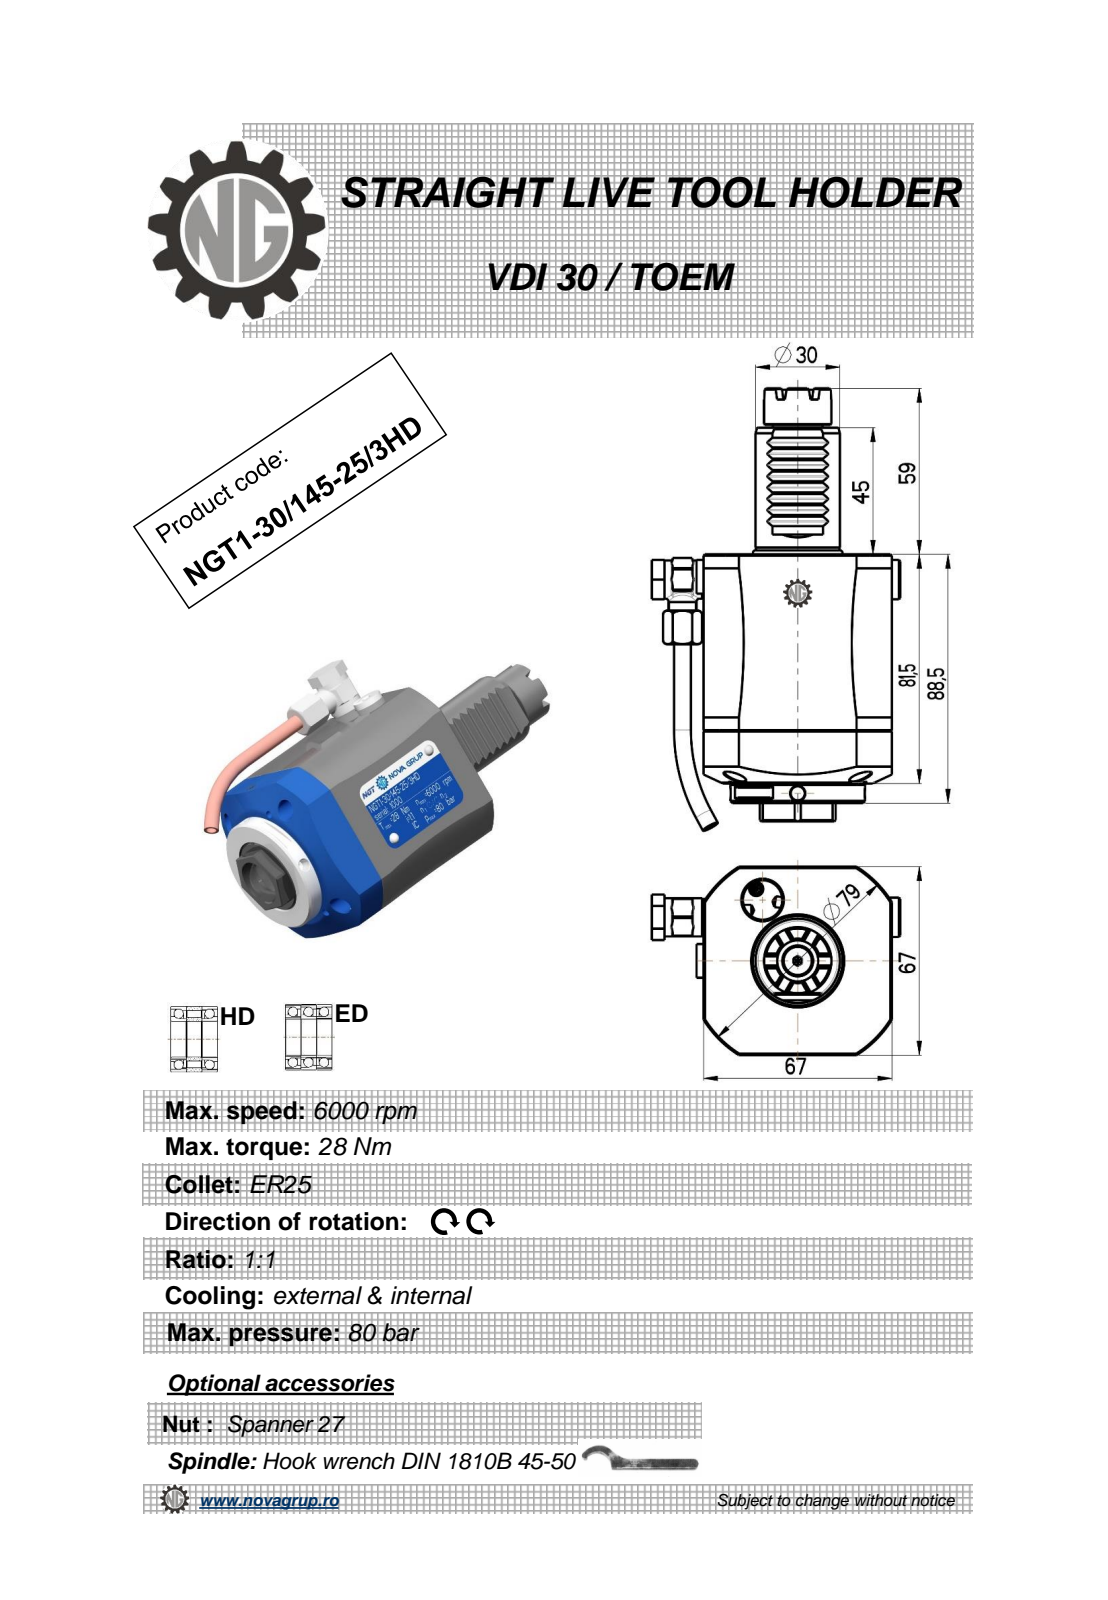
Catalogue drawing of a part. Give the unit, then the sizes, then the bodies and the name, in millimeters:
Units: millimetres
Overall size (bounding box): 157.33 × 88.4 × 67
Round holes (diameter × count): ⌀4 ×3, ⌀5 ×2, ⌀3 ×1, ⌀6 ×1, ⌀6.2 ×1, ⌀9 ×1, ⌀10 ×1, ⌀11 ×1, ⌀18 ×1, ⌀26.5 ×1
Round bosses / shafts (diameter × count): ⌀48 ×1, ⌀30 ×1, ⌀24 ×1, ⌀17.7 ×1, ⌀14 ×1, ⌀13.6 ×1, ⌀13 ×1, ⌀12 ×1
Partial cylindrical surfaces — rounded edges, fillets, slot ends (radius × count): R0.3 ×8, R0.41 ×6, R0.5 ×4, R7.6 ×1, R7.7 ×1, R39.5 ×1
Main face-to-face distances: 67, 88.5, 7, 81.5, 2.83, 13.5, 140, 133.5, 126.5, 45
Hole centre spacings: 0.4, 43.83, 44.21, 77.56
Volume: 388 507 mm³ · Surface area: 41 930 mm²
Bodies: 2 solids, 402 faces (168 planar, 107 cylindrical, 127 other)
Part name (STEP PRODUCT): NGT1_30_145_25_3HD
STEP written by: PRO/ENGINEER BY PARAMETRIC TECHNOLOGY CORPORATION, 2010280 (CONFIG_CONTROL_DESIGN)
